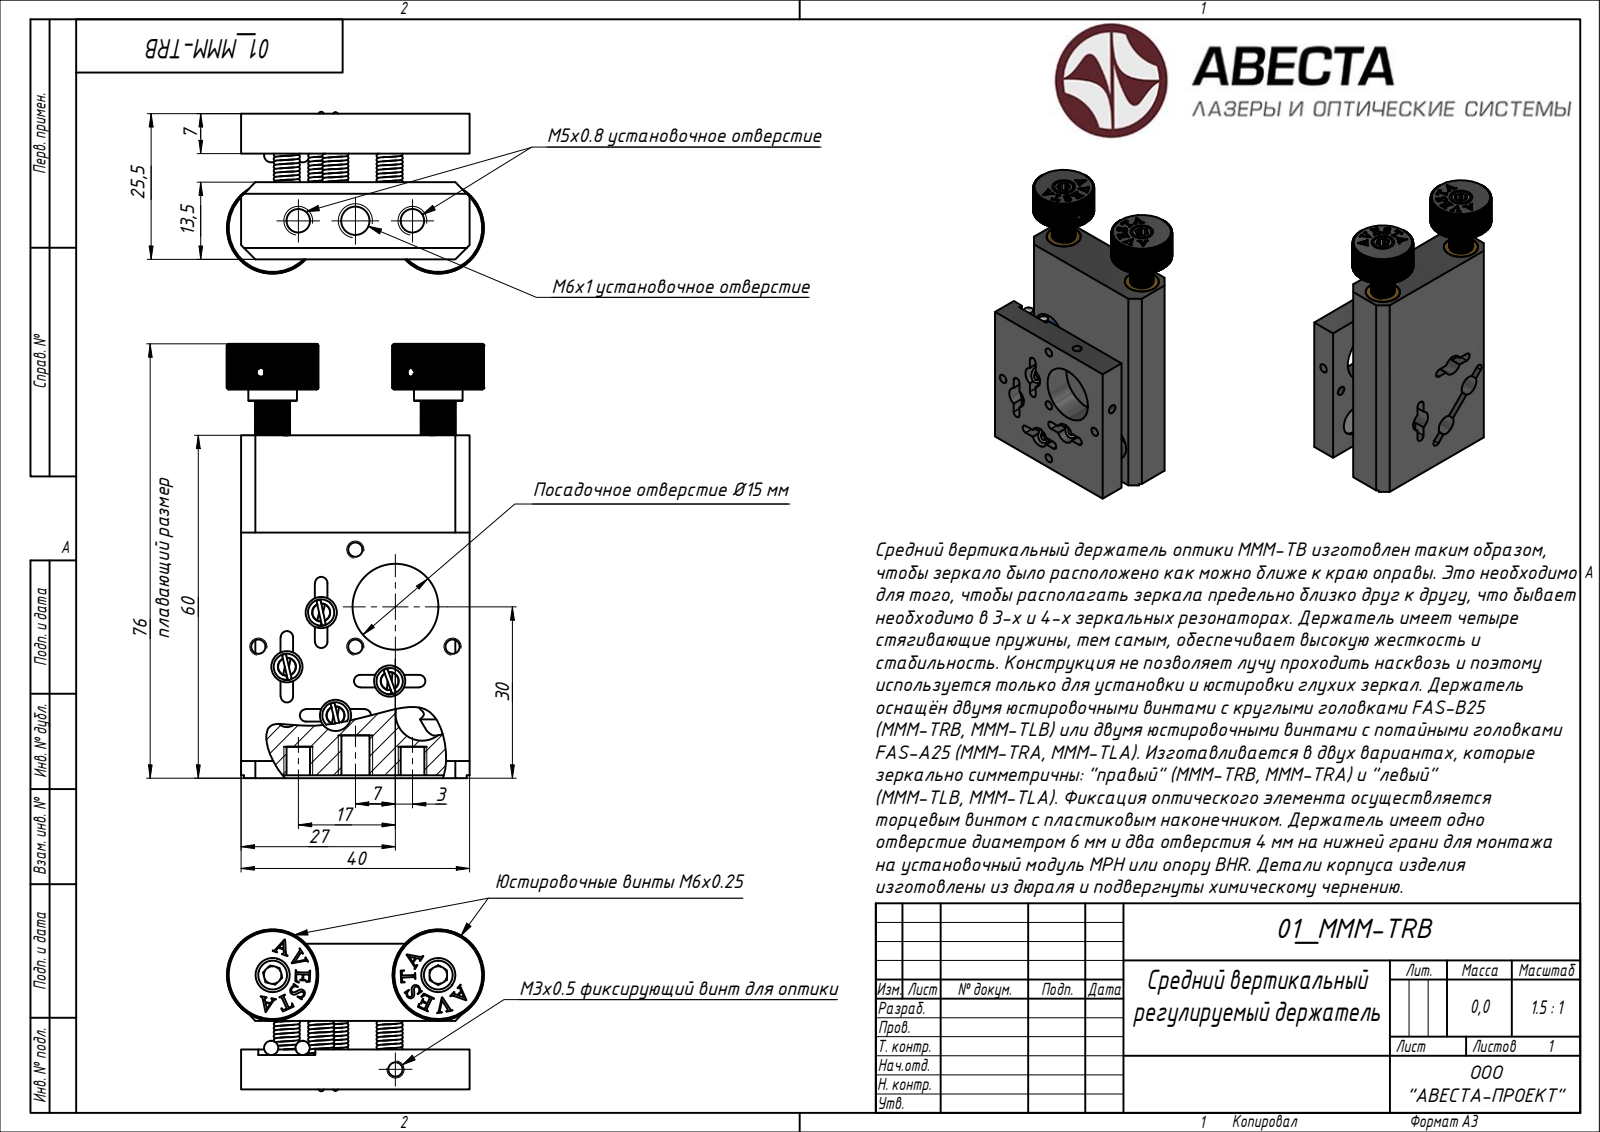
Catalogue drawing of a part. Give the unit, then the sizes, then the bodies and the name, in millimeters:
Units: millimetres
Overall size (bounding box): 78.61 × 45 × 28
Main face-to-face distances: 13.5, 12, 25.5, 7, 5, 18.5, 40, 2.5, 3, 34.29
Volume: 38 791 mm³ · Surface area: 21 203 mm²
Bodies: 11 solids, 629 faces (312 planar, 0 cylindrical, 317 other)
STEP written by: ST-DEVELOPER v15 (AUTOMOTIVE_DESIGN)
